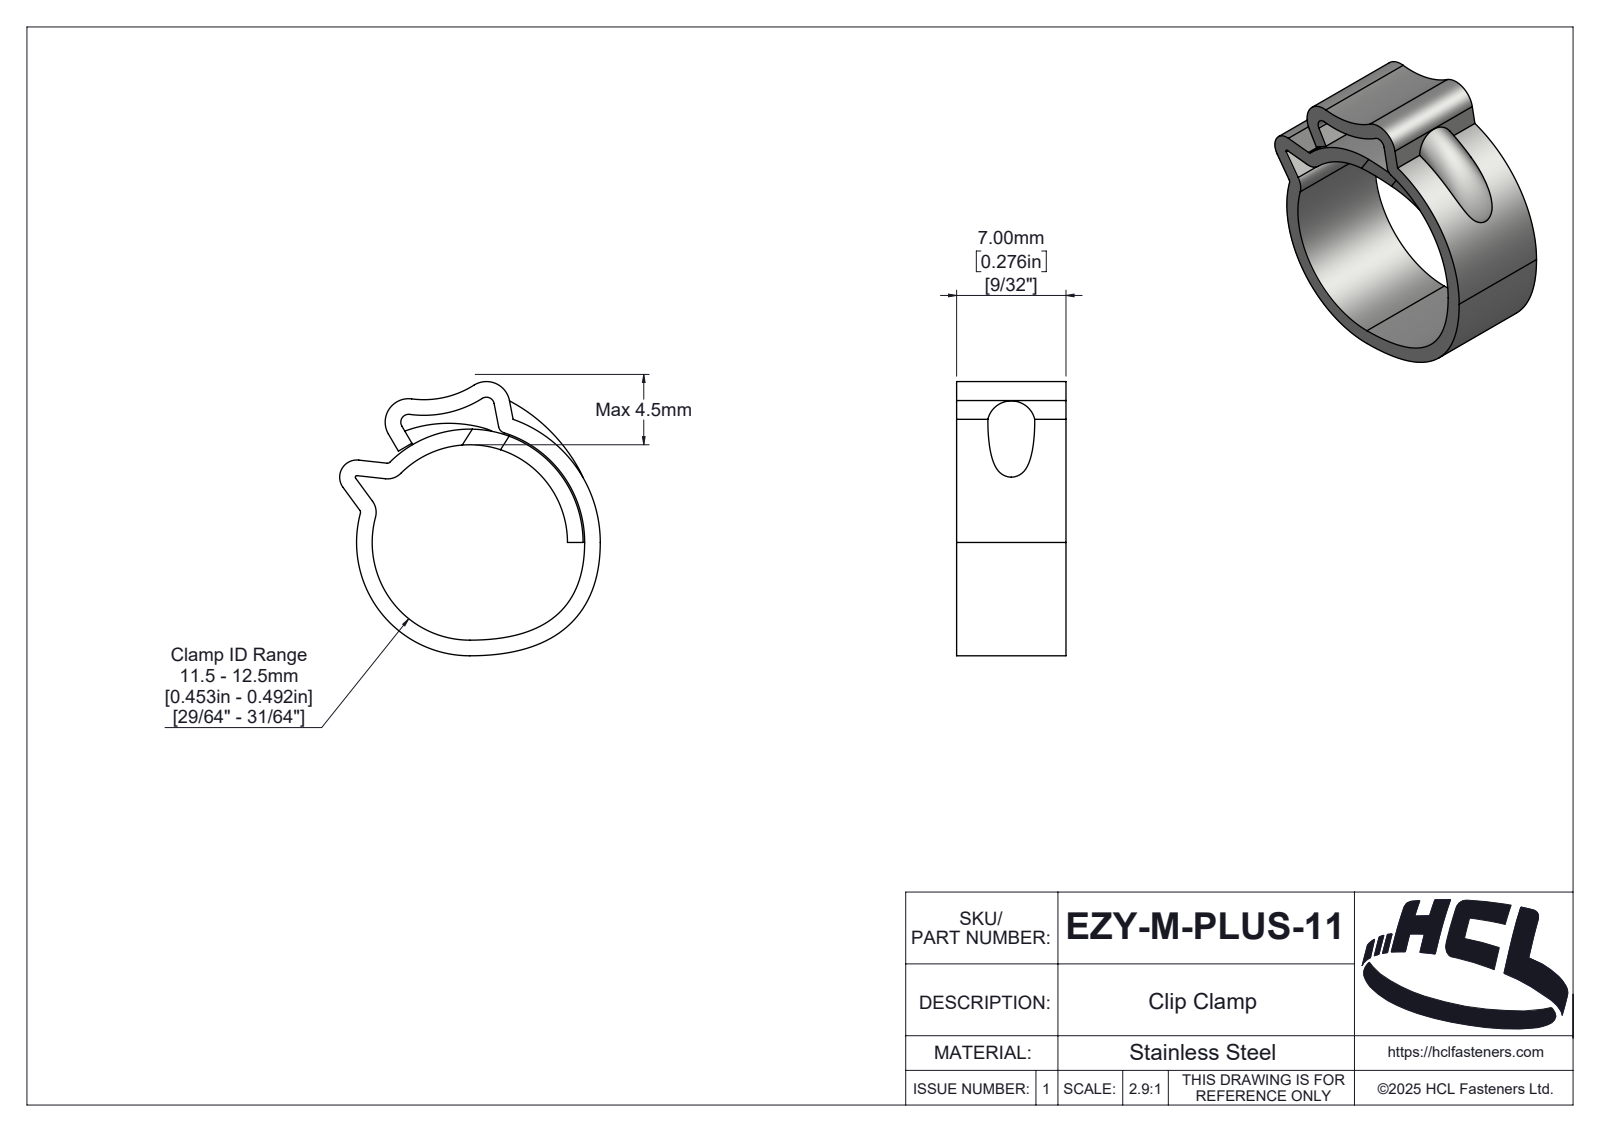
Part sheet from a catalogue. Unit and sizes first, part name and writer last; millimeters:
Units: millimetres
Overall size (bounding box): 17.54 × 16.68 × 7
Partial cylindrical surfaces — rounded edges, fillets, slot ends (radius × count): R0.5 ×3, R0.2 ×2, R1.2 ×2, R1.5 ×2, R10 ×2, R0.1 ×1, R0.23 ×1, R0.94 ×1
Main face-to-face distances: 7, 1
Volume: 466 mm³ · Surface area: 1 063 mm²
Bodies: 1 solid, 154 faces (17 planar, 74 cylindrical, 63 other)
Part name (STEP PRODUCT): EZY-M-PLUS-11
STEP written by: SolidWorks 2025 (AUTOMOTIVE_DESIGN)
